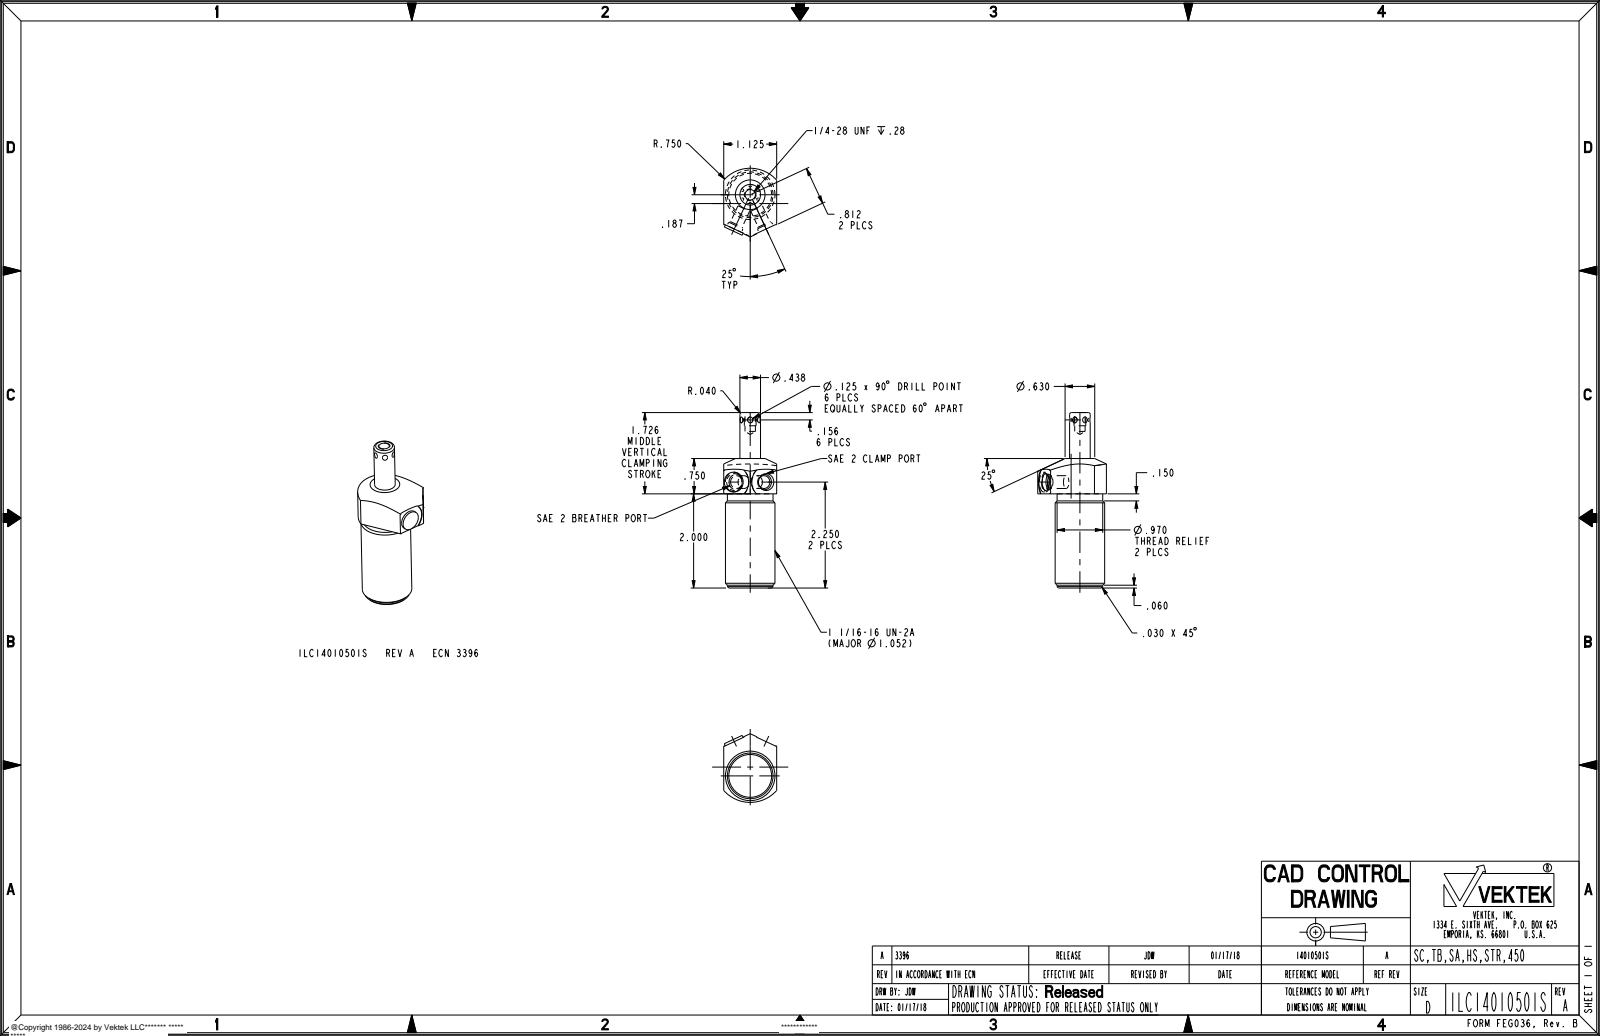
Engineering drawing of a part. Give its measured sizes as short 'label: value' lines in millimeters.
name: ILC14010501S
written by: PRO/ENGINEER BY PARAMETRIC TECHNOLOGY CORPORATION, 2013320 (AUTOMOTIVE_DESIGN)
unit: mm
bodies: 1 solid, 76 faces (19 planar, 25 cylindrical, 32 other)
size: 94.6 × 37.1 × 28.6
volume: 44 470 mm³; area: 9 671 mm²
holes: 2× ⌀6.9, 1× ⌀5.6
bosses: 1× ⌀26.7, 1× ⌀24.6, 1× ⌀11.1, 1× ⌀10.6, 1× ⌀6.4
rounds: 2× R8.7, 1× R19.1
face distances: 50.8, 28.6, 69.9, 19.1, 1.3, 12.2, 1.3, 94.6, 43.8, 24.8
